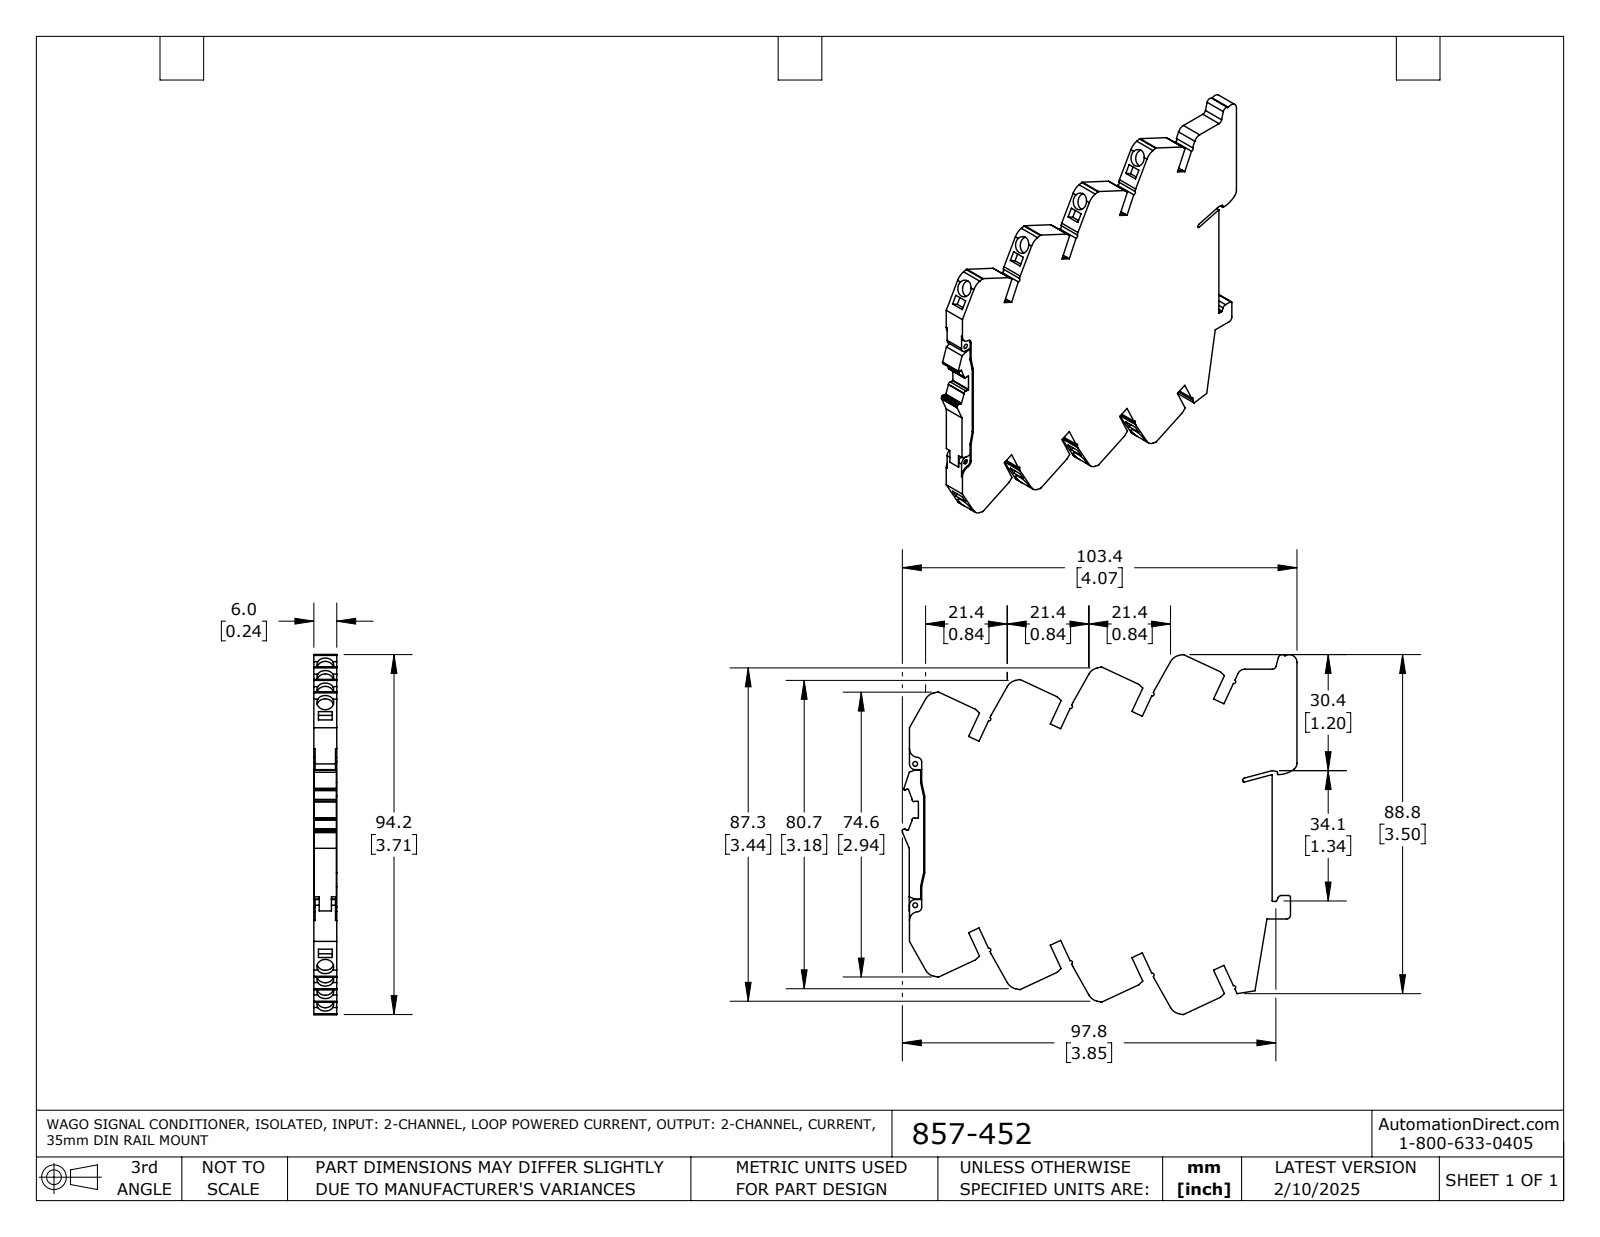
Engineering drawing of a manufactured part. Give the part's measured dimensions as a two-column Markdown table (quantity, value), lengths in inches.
| quantity | value |
| --- | --- |
| part name | 857-452 |
| STEP written by | SolidWorks 2021 (AUTOMOTIVE_DESIGN) |
| units | inches |
| bodies | 1 solid, 317 faces (219 planar, 98 cylindrical, 0 other) |
| overall size | 4.069 × 3.711 × 0.236 |
| volume | 2.681 in³ |
| surface area | 29.86 in² |
| round holes (diameter × count) | 0.173 × 8, 0.049 × 2 |
| partial cylindrical surfaces (radius × count) | 0.02 × 12, 0.008 × 11, 0.016 × 8, 0.132 × 8, 0.039 × 4, 0.012 × 3, 0.079 × 3, 0.018 × 2 |
| main face-to-face distances | 0.236, 0.708, 0.67, 0.473, 0.232, 0.472, 0.118, 0.945, 1.417, 0.256 |
| hole center spacings | 0.526, 0.525, 1.051, 1.051, 1.052, 1.457, 1.576, 1.577 |
